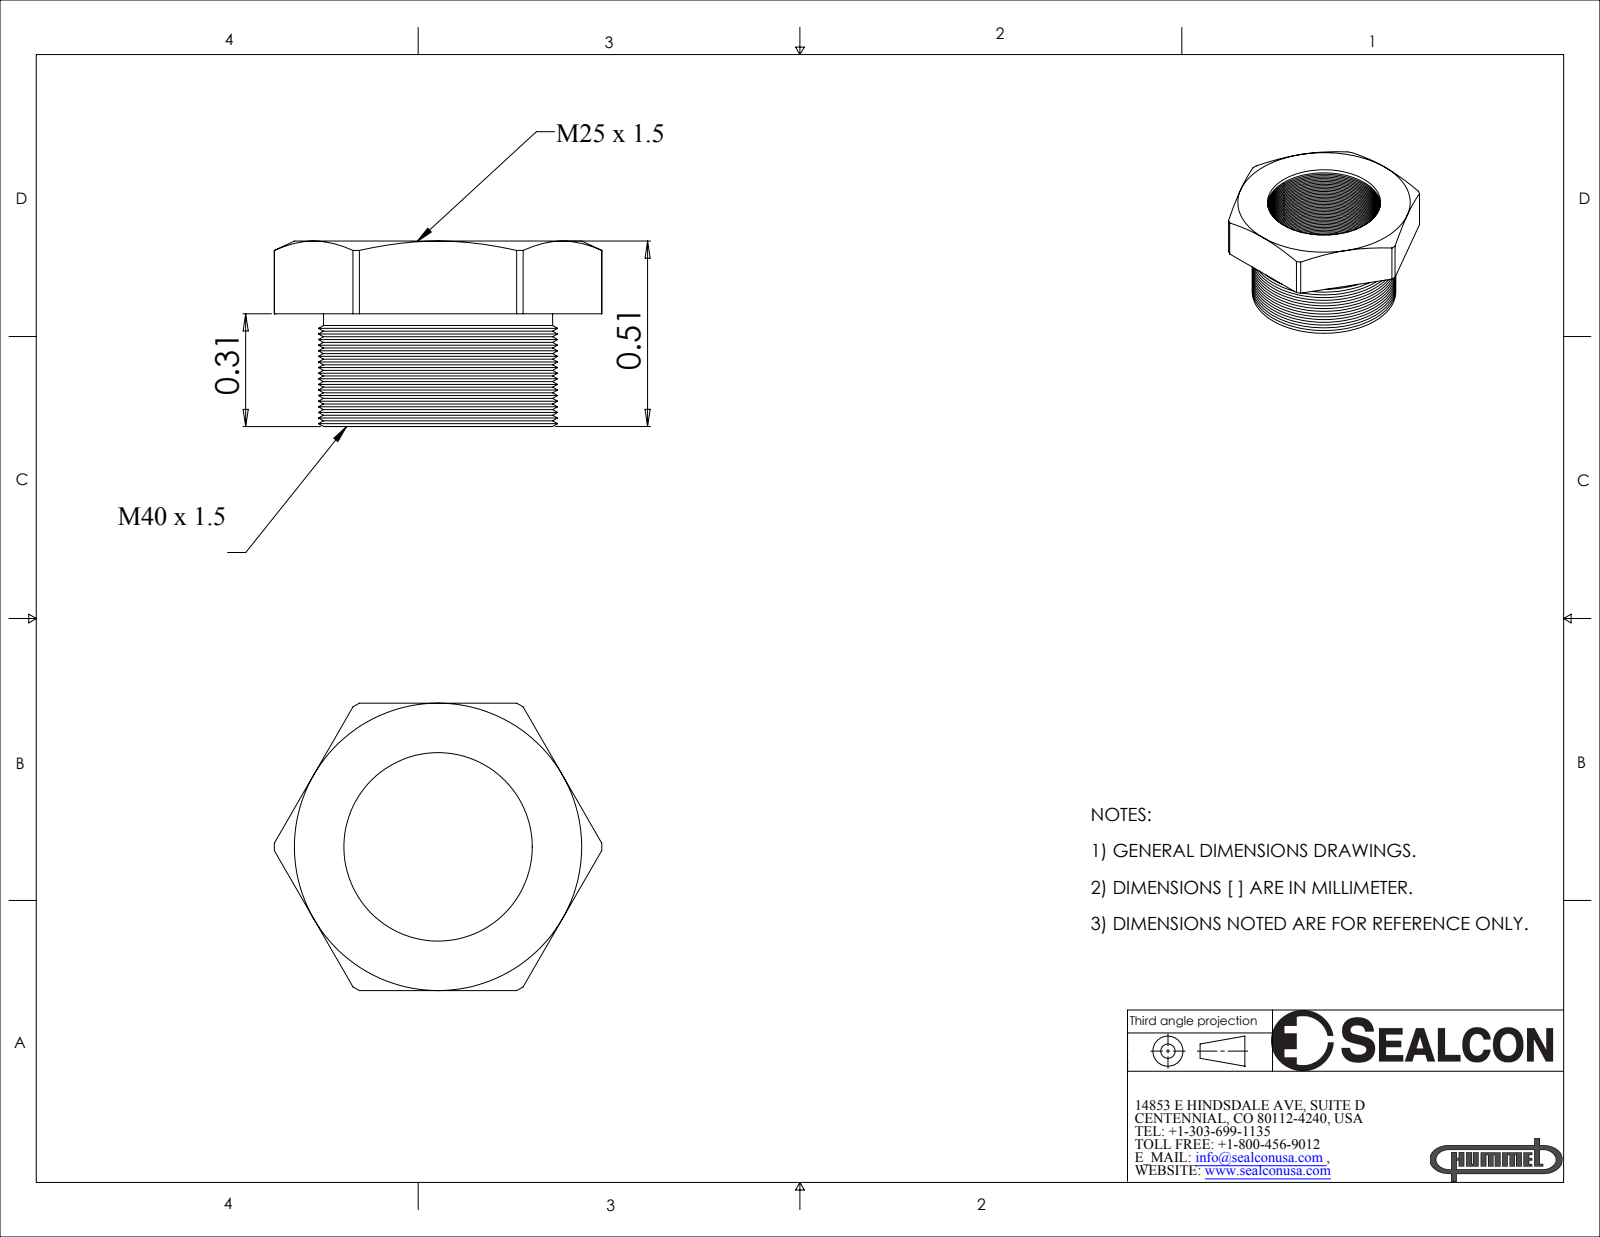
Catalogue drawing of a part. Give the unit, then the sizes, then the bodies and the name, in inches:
Units: inches
Overall size (bounding box): 0.901 × 0.79 × 0.51
Round holes (diameter × count): ⌀0.518 ×1
Round bosses / shafts (diameter × count): ⌀0.63 ×1
Partial cylindrical surfaces — rounded edges, fillets, slot ends (radius × count): R0.45 ×1
Main face-to-face distances: 0.79, 0.2, 0.31, 0.51
Volume: 0.098 in³ · Surface area: 4.047 in²
Bodies: 1 solid, 287 faces (9 planar, 75 cylindrical, 203 other)
Part name (STEP PRODUCT): RM-4025-SS
STEP written by: SolidWorks 2008 (CONFIG_CONTROL_DESIGN)
